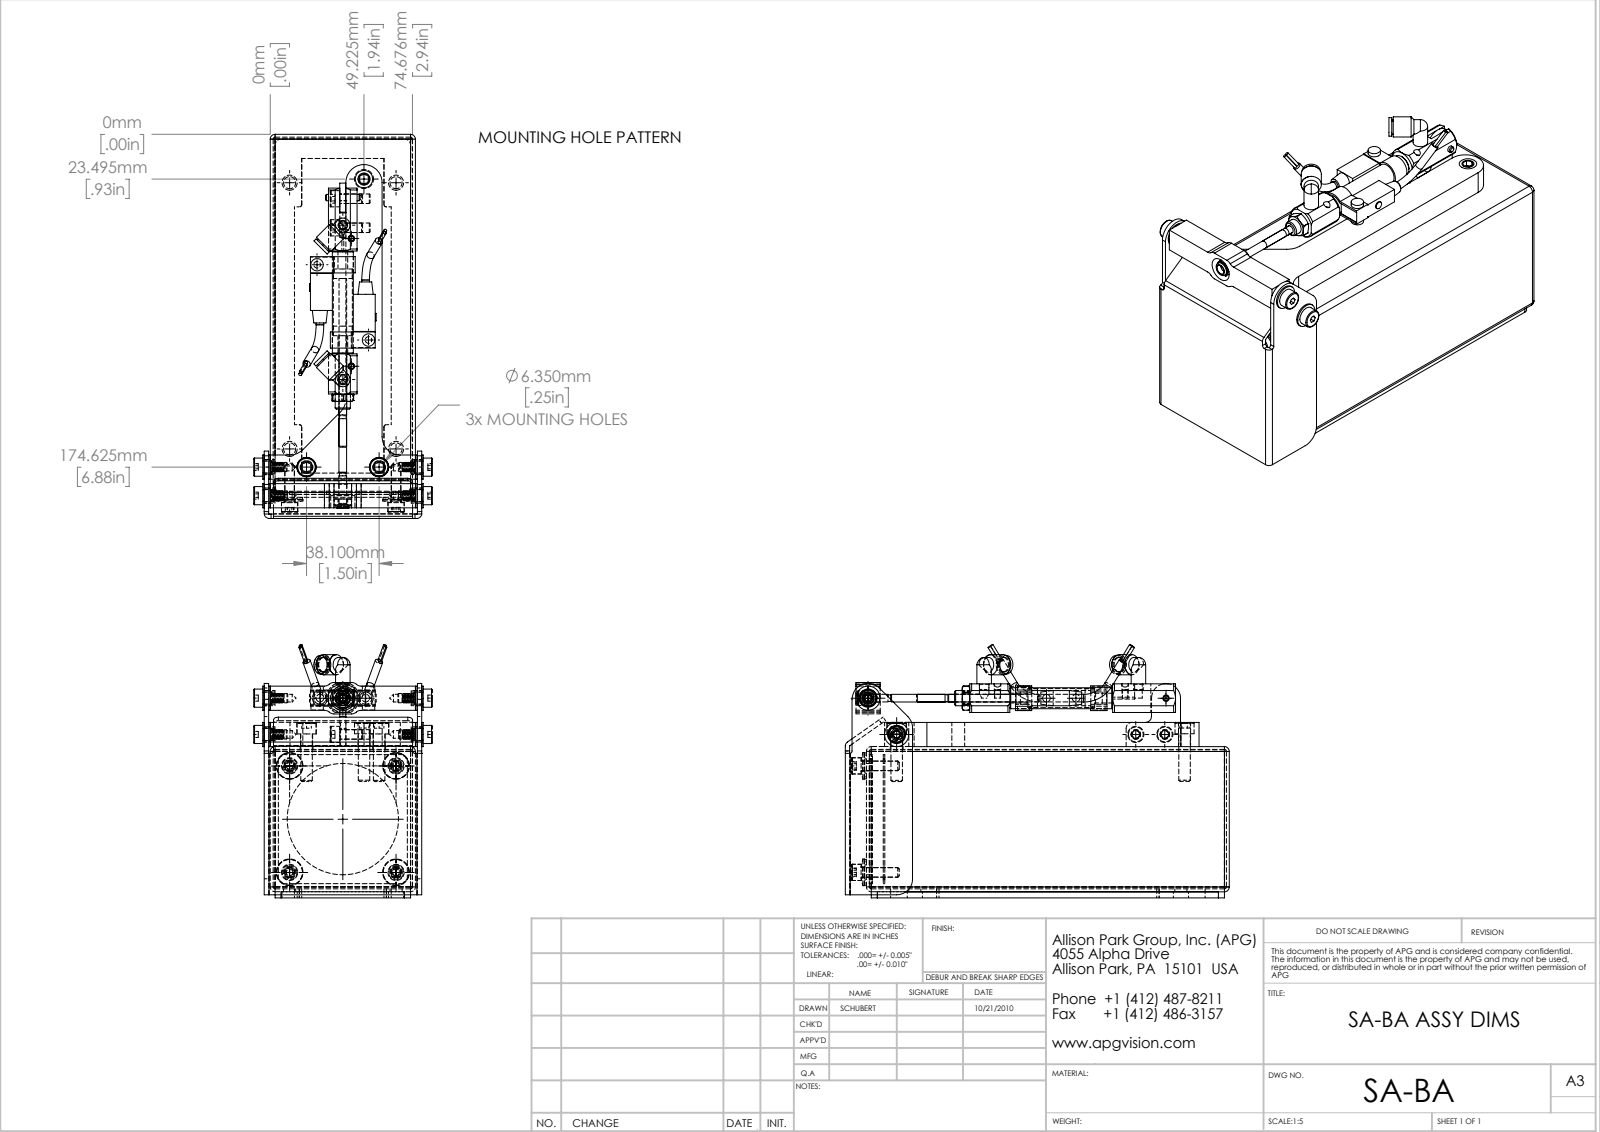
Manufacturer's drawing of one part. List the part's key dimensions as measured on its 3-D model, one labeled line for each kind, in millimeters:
Part name (STEP PRODUCT): SA-BA Assembly
STEP written by: SolidWorks 2014 (CONFIG_CONTROL_DESIGN)
Units: millimetres
Bodies: 44 solids, 1312 faces (386 planar, 573 cylindrical, 353 other)
Overall size (bounding box): 201.55 × 132.98 × 93.81
Volume: 239 169 mm³ · Surface area: 218 207 mm²
Round holes (diameter × count): ⌀6.35 ×12, ⌀7.95 ×8, ⌀5 ×5, ⌀4.04 ×4, ⌀5.16 ×4, ⌀5.37 ×4, ⌀5.82 ×4, ⌀6.6 ×4, ⌀3.5 ×2, ⌀6.73 ×2, ⌀10.16 ×2, ⌀1 ×1
Round bosses / shafts (diameter × count): ⌀4 ×7, ⌀8.5 ×6, ⌀12.7 ×5, ⌀5 ×5, ⌀14 ×4, ⌀7.94 ×4, ⌀7.62 ×4, ⌀4.83 ×4
Partial cylindrical surfaces — rounded edges, fillets, slot ends (radius × count): R2.54 ×21, R1.02 ×12, R3.81 ×9, R1.27 ×7, R3.17 ×6, R8.38 ×4, R9.53 ×4, R0.25 ×3
Main face-to-face distances: 1.52, 74.68, 76.2, 73.16, 2.29, 12.7, 3.17, 14.22, 199.26, 201.55
Hole centre spacings: 55.88, 39.51, 79.03, 45.22, 24.25, 156.95, 13.03, 15.24
